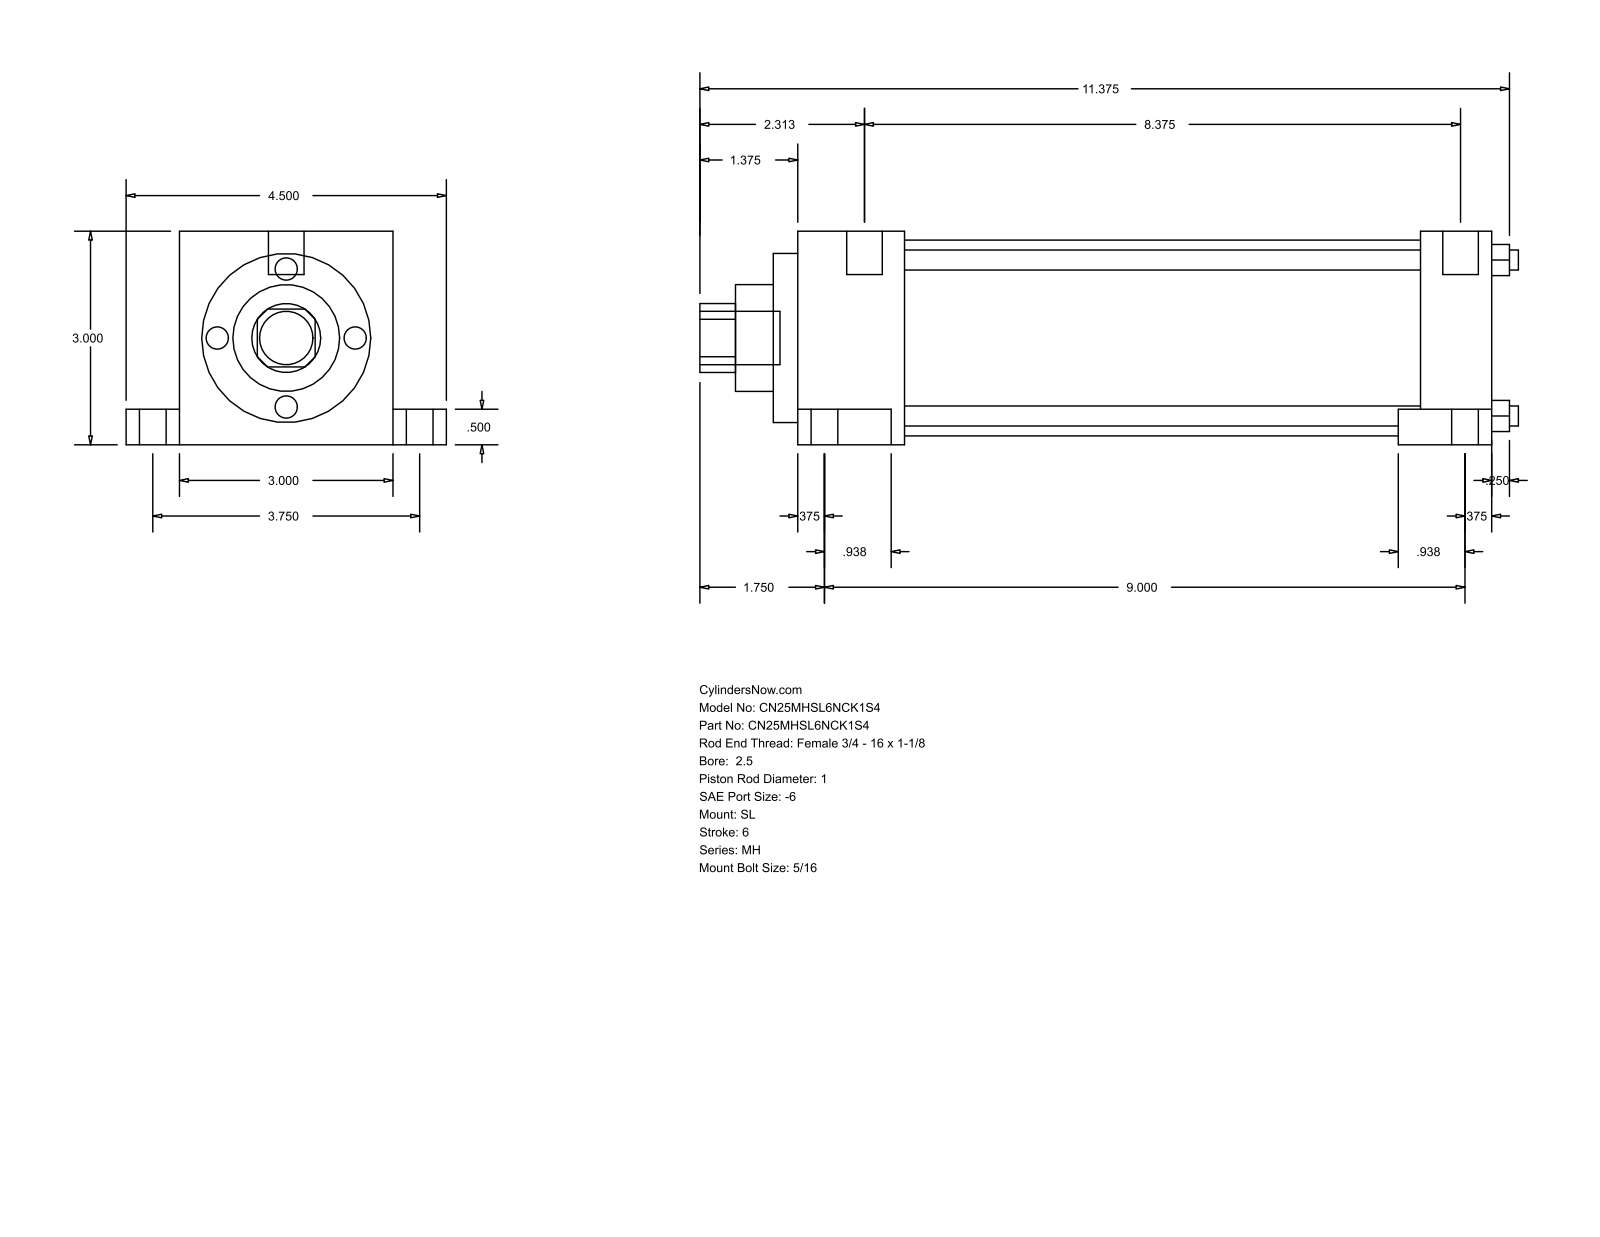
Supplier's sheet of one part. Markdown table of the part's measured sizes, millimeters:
| quantity | value |
| --- | --- |
| part name | MH_SL__0250_1 |
| STEP written by | GSSL Pune (CONFIG_CONTROL_DESIGN) |
| units | millimeters |
| bodies | 0 solids, 86 faces (61 planar, 25 cylindrical, 0 other) |
| overall size | 292.1 × 114.3 × 76.2 |
| round holes (diameter × count) | 7.14 × 4, 25.4 × 1, 38.1 × 1, 60.33 × 1, 69.85 × 1 |
| round bosses / shafts (diameter × count) | 15.88 × 2, 9.53 × 2, 5.56 × 2, 19.05 × 1, 12.7 × 1 |
| partial cylindrical surfaces (radius × count) | 12.29 × 1 |
| main face-to-face distances | 76.2, 25.39, 230.99, 256.38, 12.7, 63.5, 19.05, 95.25, 13.49, 244.48 |
| hole center spacings | 39.33, 55.62, 78.66 |
